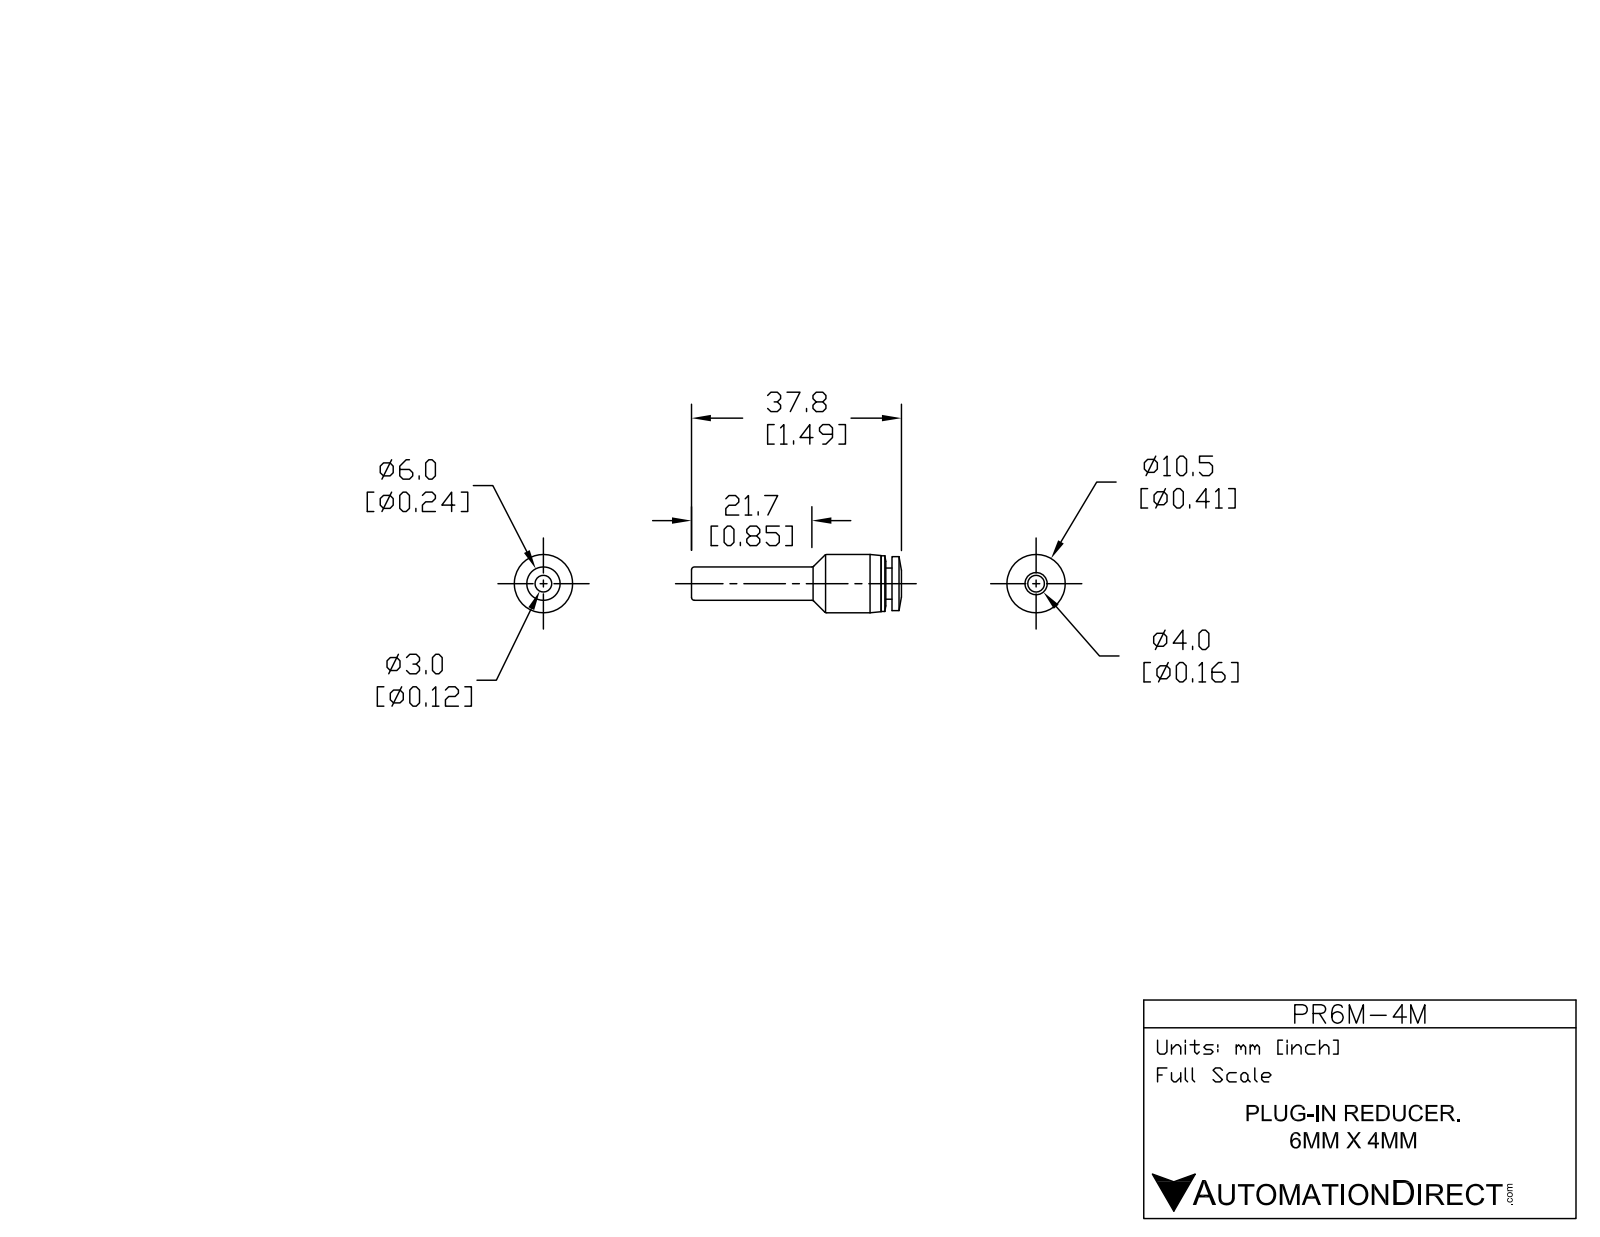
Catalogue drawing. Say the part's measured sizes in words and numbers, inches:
The part is named "PR6M-4M". Its 3-D file was written by "SolidWorks 2015 (AUTOMOTIVE_DESIGN)". It is 1 solid with 36 faces: 6 planar, 14 cylindrical and 16 other. Overall it measures 1.482 by 0.413 by 0.413 inches. Its volume is 0.087 cubic inches and its surface area 2.335 square inches. Round holes: 1 of diameter 0.118, 1 of diameter 0.169. Round bosses or shafts: 1 of diameter 0.413, 1 of diameter 0.394, 1 of diameter 0.382, 1 of diameter 0.236, 1 of diameter 0.22. The main face-to-face distances are 0.043, 1.372, 1.415, 0.9, 0.472, 0.516, 1.339, 0.439, 0.033, 0.077.
